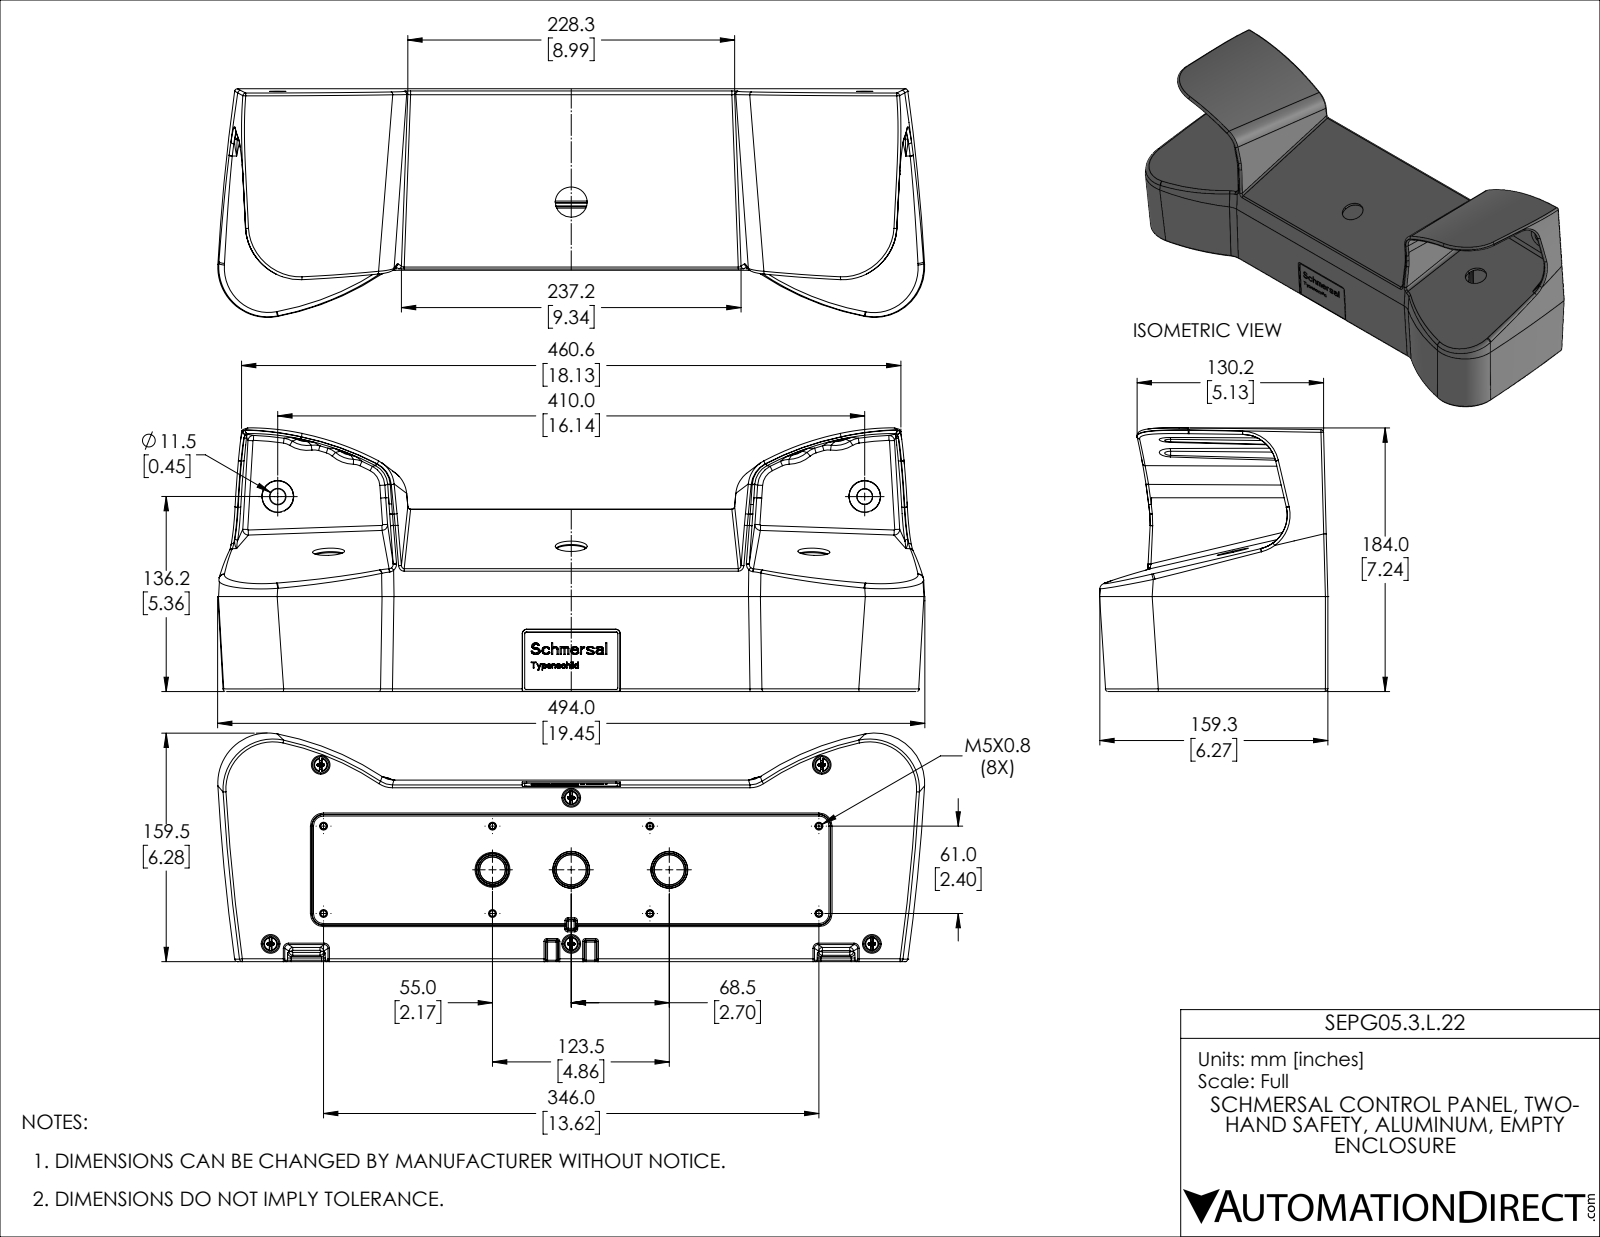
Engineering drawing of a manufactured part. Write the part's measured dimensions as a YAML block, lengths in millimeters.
part_name: "SEPG05.3.L.22_REVISION1"
step_written_by: "SolidWorks 2019 (AUTOMOTIVE_DESIGN)"
units: millimeters
bodies: {solids: 1, faces: 3709, planar: 1191, cylindrical: 774, other: 1744}
overall_size: [493.7, 184.1, 159.6]
volume: 1488000
surface_area: 651000
round_holes:
  - {diameter: 11, count: 6}
  - {diameter: 5.6, count: 2}
  - {diameter: 2.9, count: 1}
round_bosses_or_shafts:
  - {diameter: 6, count: 9}
  - {diameter: 9.6, count: 6}
  - {diameter: 6.4, count: 4}
  - {diameter: 3.5, count: 3}
  - {diameter: 2.6, count: 3}
partial_cylinders:
  - {radius: 1, count: 160}
  - {radius: 0.5, count: 76}
  - {radius: 0.1, count: 68}
  - {radius: 0.2, count: 47}
  - {radius: 0.4, count: 34}
  - {radius: 0.2, count: 31}
  - {radius: 3, count: 27}
  - {radius: 1.9, count: 25}
face_to_face_distances: [4, 4.5, 3.5, 8.5, 3.5, 0.5, 5, 1.5, 3, 10]
hole_center_spacings: [129.8, 176.5, 210, 215.1, 233.5, 404.8, 12, 21.2]
